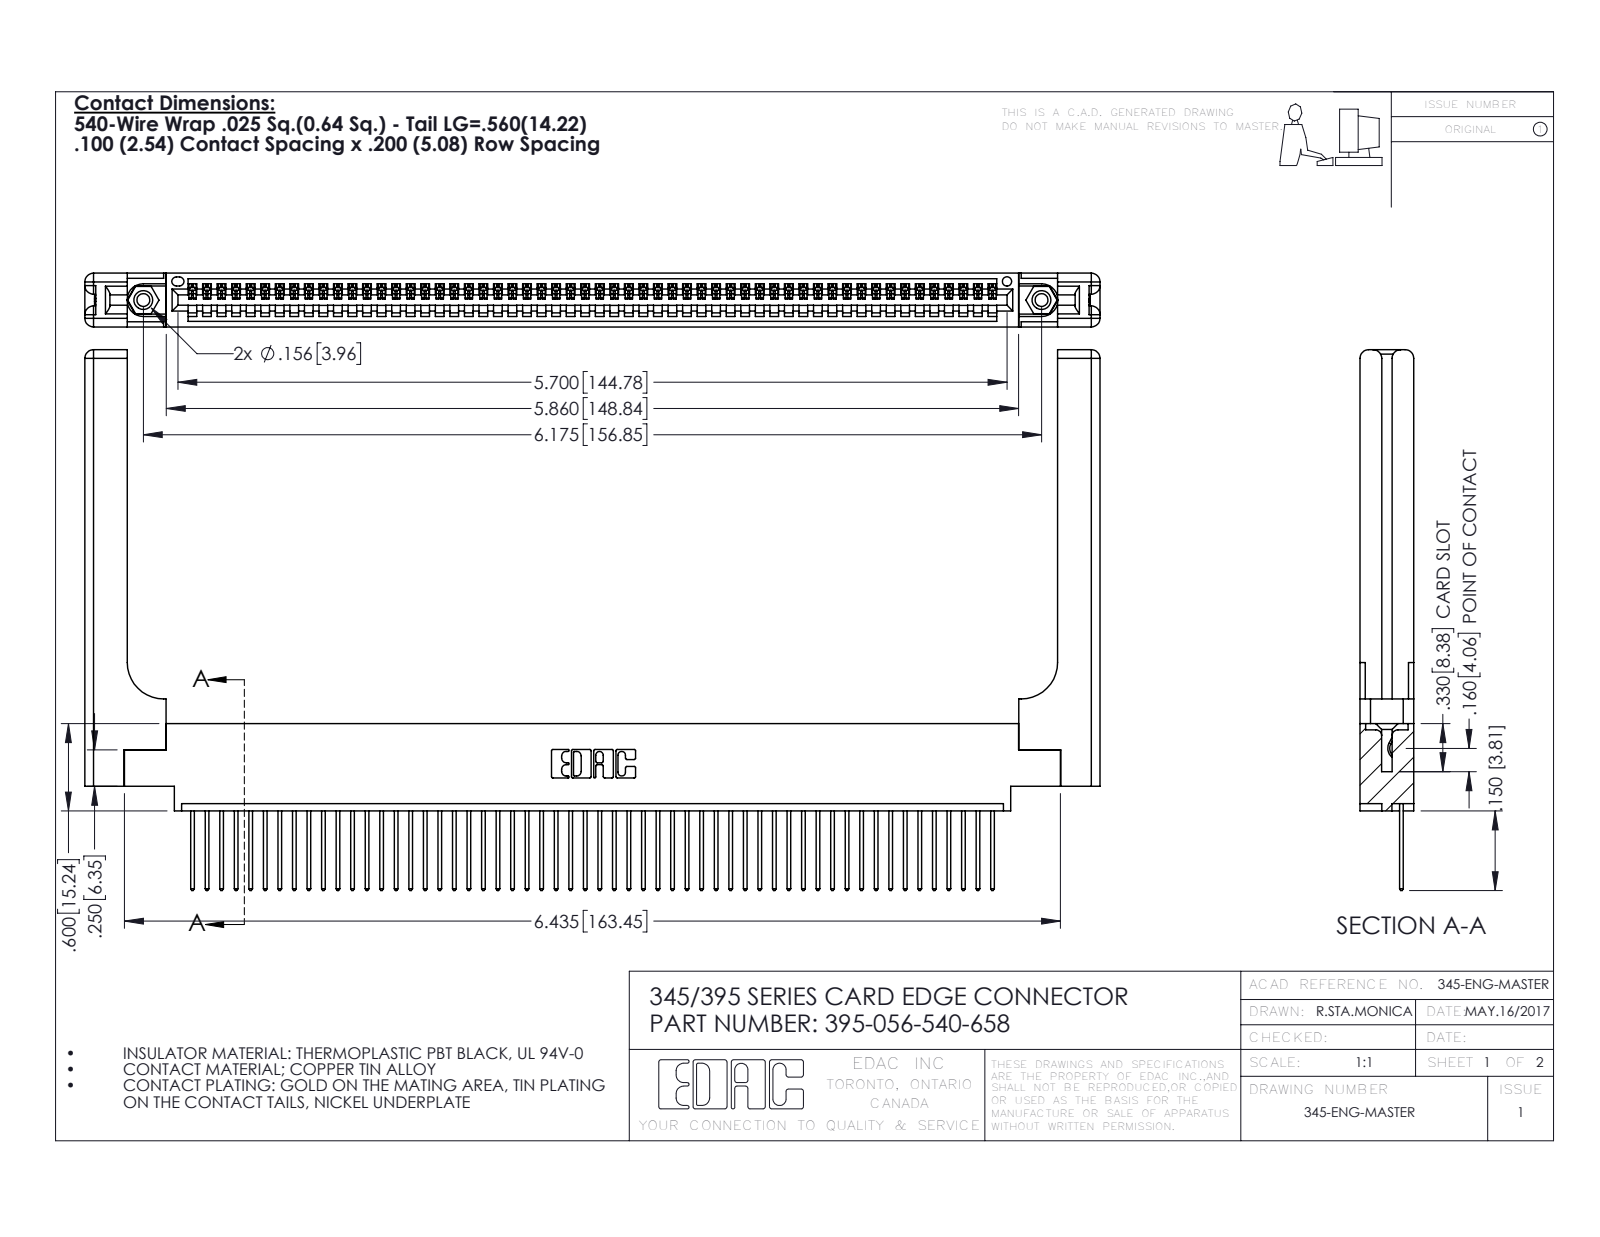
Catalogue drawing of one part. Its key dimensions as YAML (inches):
part_name: "345-292-001_345-293-140; 345-250-001_345-250-001-102; 345-220-058_345-220-058; 345 Part_0.170 Offset - 0.156 Dia-TH (+1 more)"
step_written_by: "SolidWorks 2016 (CONFIG_CONTROL_DESIGN)"
units: inches
bodies: {solids: 61, faces: 3634, planar: 2472, cylindrical: 1102, other: 60}
overall_size: [6.979, 3.717, 0.37]
volume: 1.551
surface_area: 44.4
round_holes:
  - {diameter: 0.089, count: 2}
  - {diameter: 0.125, count: 2}
  - {diameter: 0.156, count: 2}
  - {diameter: 0.064, count: 1}
round_bosses_or_shafts:
  - {diameter: 0.155, count: 2}
partial_cylinders:
  - {radius: 0.006, count: 112}
  - {radius: 0.01, count: 112}
  - {radius: 0.01, count: 22}
  - {radius: 0.06, count: 16}
  - {radius: 0.007, count: 6}
  - {radius: 0.031, count: 6}
  - {radius: 0.026, count: 3}
  - {radius: 0.03, count: 2}
face_to_face_distances: [0.072, 0.37, 0.298, 0.098, 0.272, 0.025, 0.2, 0.225, 0.148, 0.15]
hole_center_spacings: [0.27, 5.939, 6.175]
